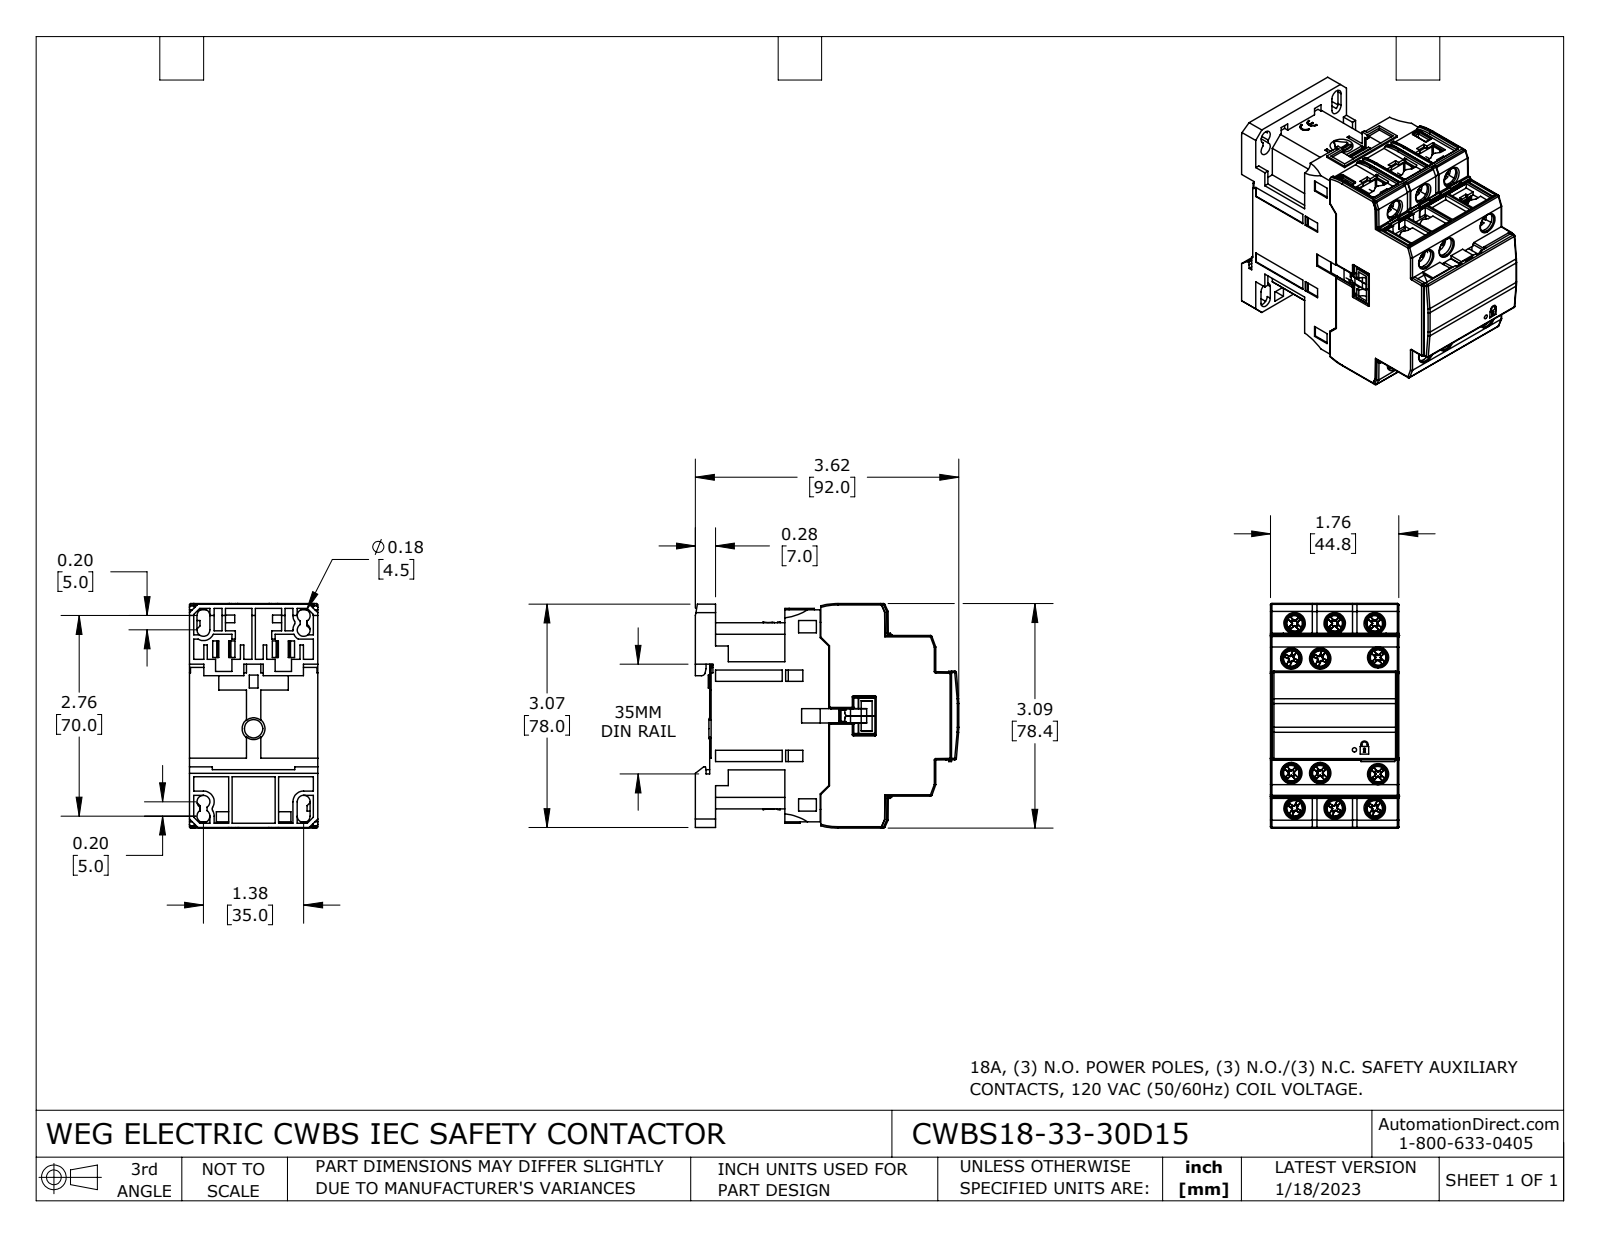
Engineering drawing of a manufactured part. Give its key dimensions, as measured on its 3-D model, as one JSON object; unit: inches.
{"part_name": "CWBS18-33-30D15", "step_written_by": "SolidWorks 2021 (CONFIG_CONTROL_DESIGN)", "units": "inches", "bodies": {"solids": 45, "faces": 3295, "planar": 2311, "cylindrical": 624, "other": 360}, "overall_size": [3.62, 3.087, 1.764], "volume_in3": 13.51, "surface_area_in2": 120.4, "round_holes": [[0.124, 12], [0.256, 6], [0.177, 4], [0.059, 1]], "round_bosses_or_shafts": [[0.169, 12], [0.138, 12], [0.107, 8], [0.107, 4]], "partial_cylinders_radius": [[0.02, 139], [0.012, 52], [0.071, 24], [0.964, 24], [2.128, 24], [0.016, 20], [0.039, 19], [0.106, 11]], "face_to_face_distances": [1.764, 0.047, 1.717, 3.305, 1.754, 1.551, 0.276, 0.022, 1.776, 1.53], "hole_center_spacings": [0.551, 1.102, 0.197, 0.398, 0.795, 1.193, 1.341, 1.575]}
